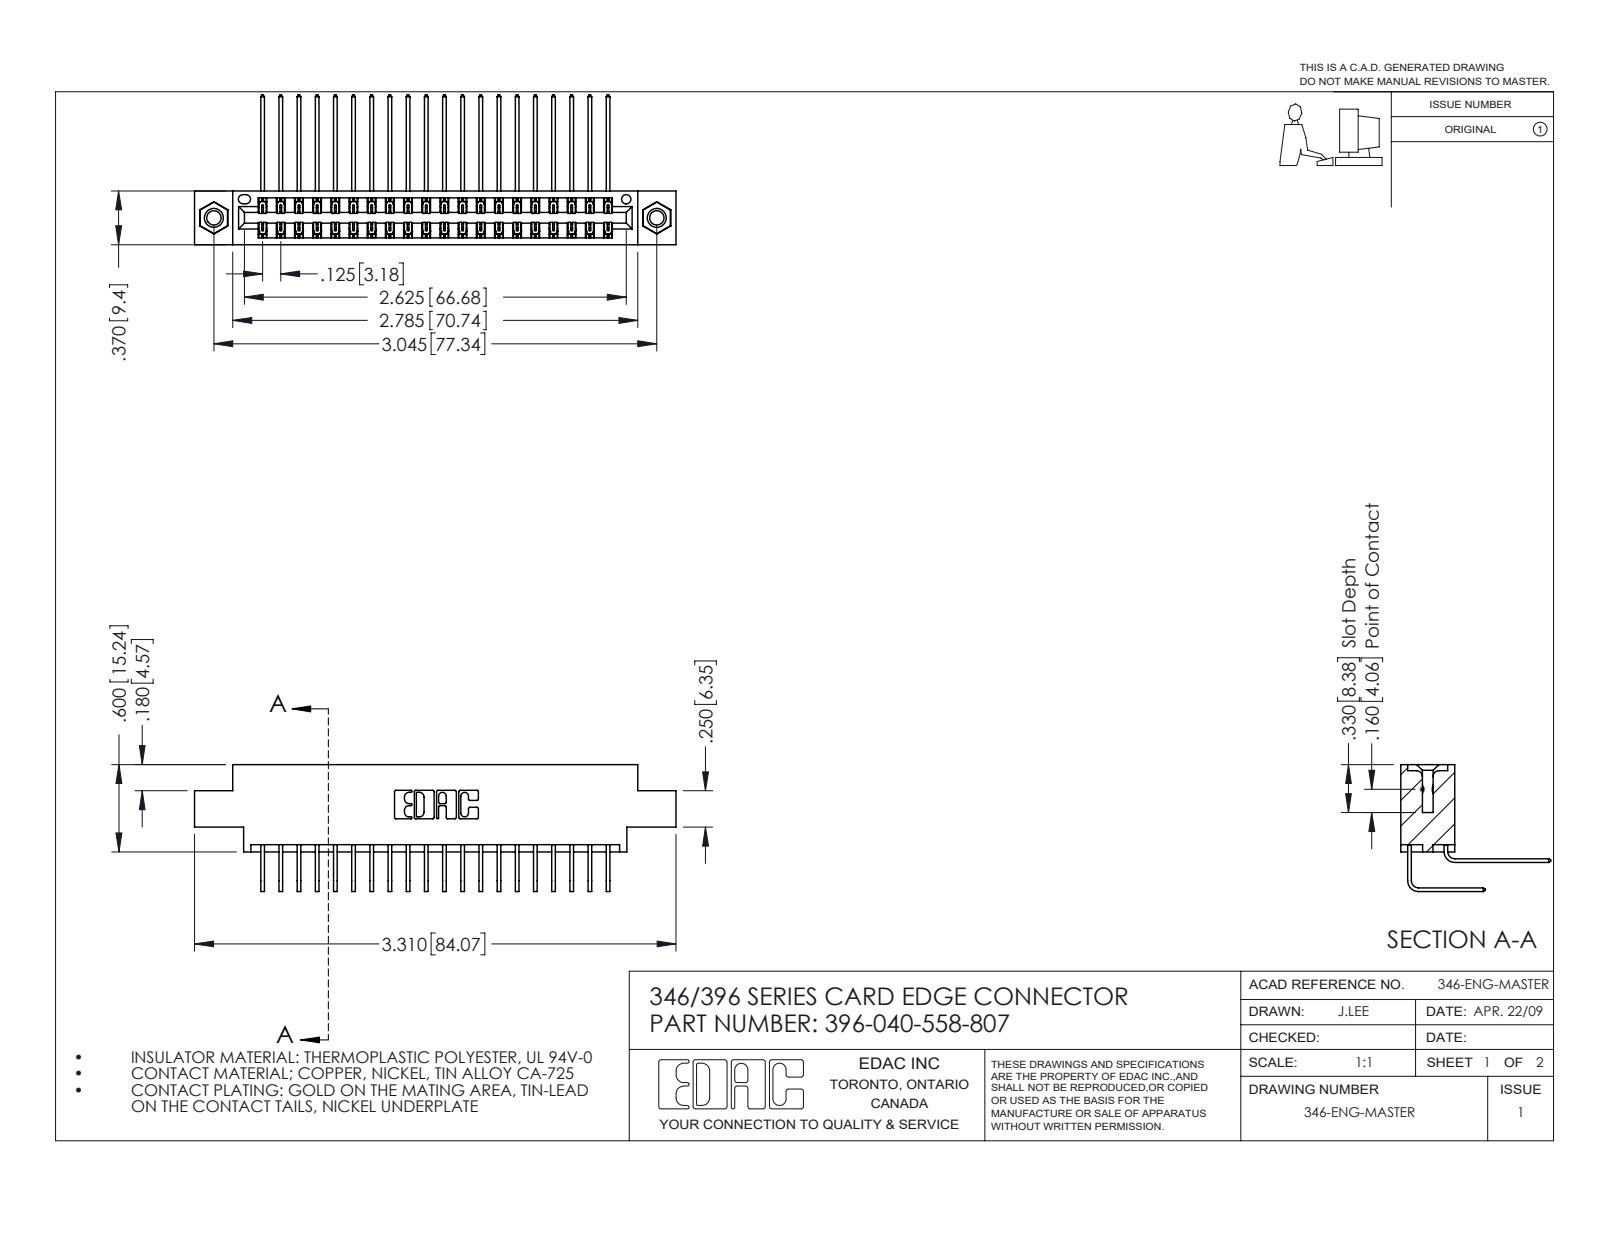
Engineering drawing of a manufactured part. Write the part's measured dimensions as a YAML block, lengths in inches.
part_name: "346 Part_0.170 Offset - 0.156 Dia-TI; 345-292-001_558 Tail - 2; 345-250-001_345-250-005-103; 396-040-558-807 (+1 more)"
step_written_by: "SolidWorks 2016 (CONFIG_CONTROL_DESIGN)"
units: inches
bodies: {solids: 43, faces: 2346, planar: 1592, cylindrical: 738, other: 16}
overall_size: [3.31, 1.03, 0.873]
volume: 0.494
surface_area: 18.75
round_holes:
  - {diameter: 0.098, count: 2}
  - {diameter: 0.125, count: 2}
  - {diameter: 0.156, count: 2}
  - {diameter: 0.064, count: 1}
round_bosses_or_shafts:
  - {diameter: 0.155, count: 2}
partial_cylinders:
  - {radius: 0.006, count: 60}
  - {radius: 0.01, count: 22}
  - {radius: 0.007, count: 6}
  - {radius: 0.031, count: 6}
  - {radius: 0.026, count: 3}
  - {radius: 0.014, count: 2}
  - {radius: 0.022, count: 2}
  - {radius: 0.024, count: 2}
face_to_face_distances: [0.322, 0.048, 0.37, 0.025, 0.25, 0.298, 0.072, 0.275, 0.222, 0.148]
hole_center_spacings: [0.246, 2.837, 3.045]
